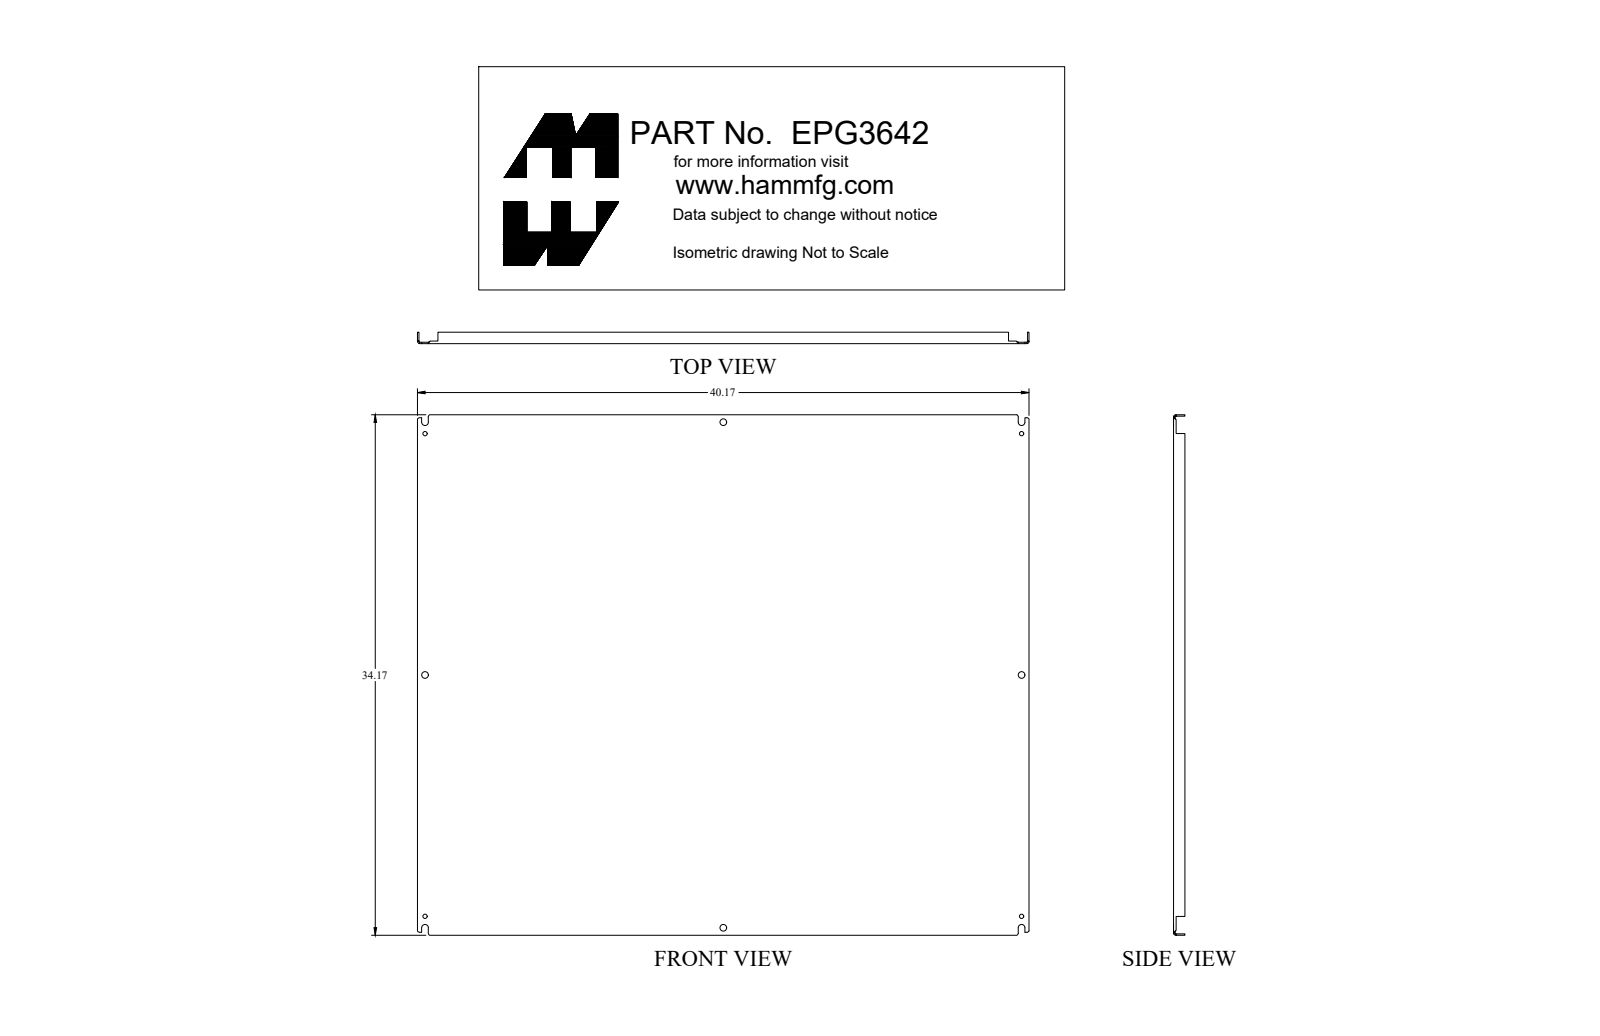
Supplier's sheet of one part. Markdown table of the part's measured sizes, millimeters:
| quantity | value |
| --- | --- |
| part name | EPG3642 |
| STEP written by | SolidWorks 2018 (AUTOMOTIVE_DESIGN) |
| units | millimeters |
| bodies | 1 solid, 136 faces (74 planar, 46 cylindrical, 16 other) |
| overall size | 1020.3 × 867.9 × 19.1 |
| volume | 2 266 000 mm³ |
| surface area | 1 888 000 mm² |
| round holes (diameter × count) | 7.1 × 4, 11.1 × 4 |
| partial cylindrical surfaces (radius × count) | 1.2 × 4, 1.6 × 4, 3.6 × 4, 5.6 × 4 |
| main face-to-face distances | 2.4, 865.5, 1017.9, 867.9, 863.1, 1015.5, 1020.3, 19.1, 16.6, 4.3 |
| hole center spacings | 402.4, 498, 652.2, 962.6, 1073.7, 995.4, 804.9, 1280.1 |
